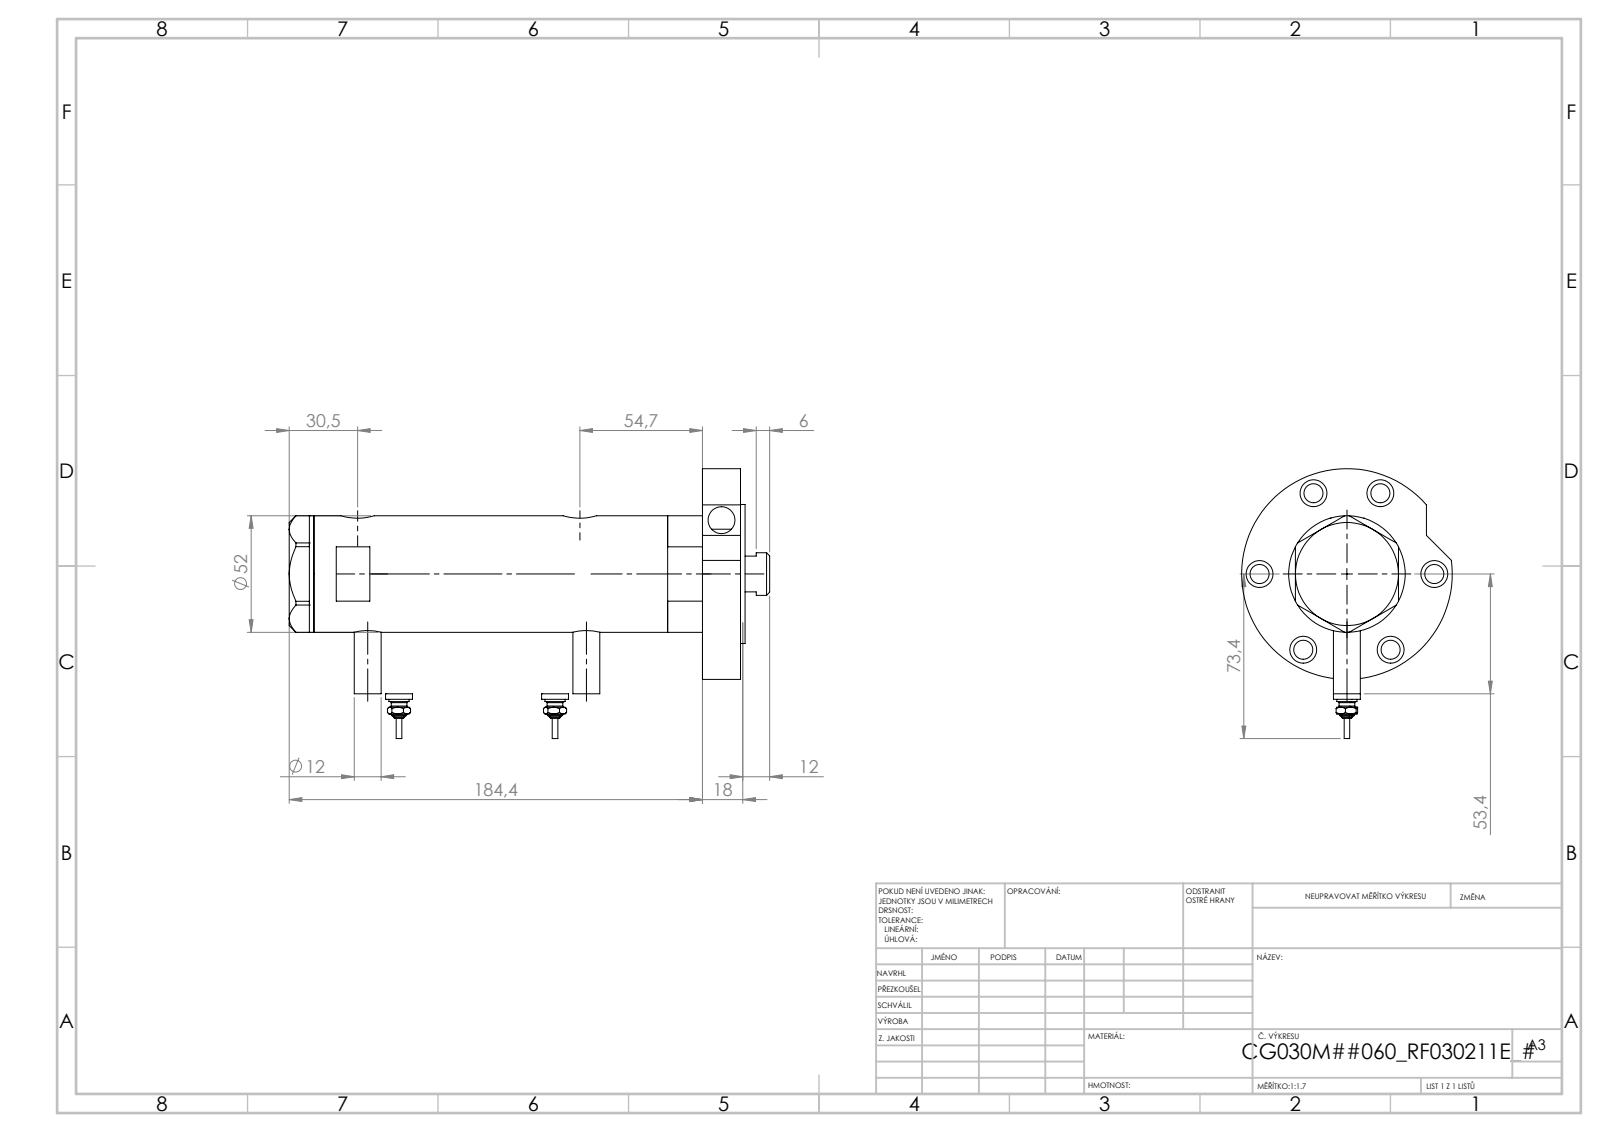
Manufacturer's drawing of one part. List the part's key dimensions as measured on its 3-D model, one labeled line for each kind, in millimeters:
Part name (STEP PRODUCT): V270CG_BACK; V270CG_MIDDLE; V270CG_VC; V270CG_FRONT (+2 more)
STEP written by: SolidWorks 2019 (CONFIG_CONTROL_DESIGN)
Units: millimetres
Bodies: 7 solids, 290 faces (106 planar, 110 cylindrical, 74 other)
Overall size (bounding box): 209.02 × 105.3 × 94
Volume: 456 048 mm³ · Surface area: 110 044 mm²
Round holes (diameter × count): ⌀12 ×7, ⌀8.5 ×6, ⌀5 ×2, ⌀9.73 ×2, ⌀12.5 ×2, ⌀15 ×2, ⌀6.5 ×1, ⌀20 ×1, ⌀21.5 ×1, ⌀30 ×1, ⌀33 ×1, ⌀40 ×1
Round bosses / shafts (diameter × count): ⌀12 ×3, ⌀9 ×2, ⌀7 ×2, ⌀4.34 ×2, ⌀2.4 ×2, ⌀94 ×1, ⌀62 ×1, ⌀52 ×1
Main face-to-face distances: 17, 51.9, 2, 68.9, 70.9, 19, 23.8, 124.55, 176.45, 193.45
Hole centre spacings: 39, 2.9, 4.5, 43.34, 64.85, 67.55, 69.95, 77.83
